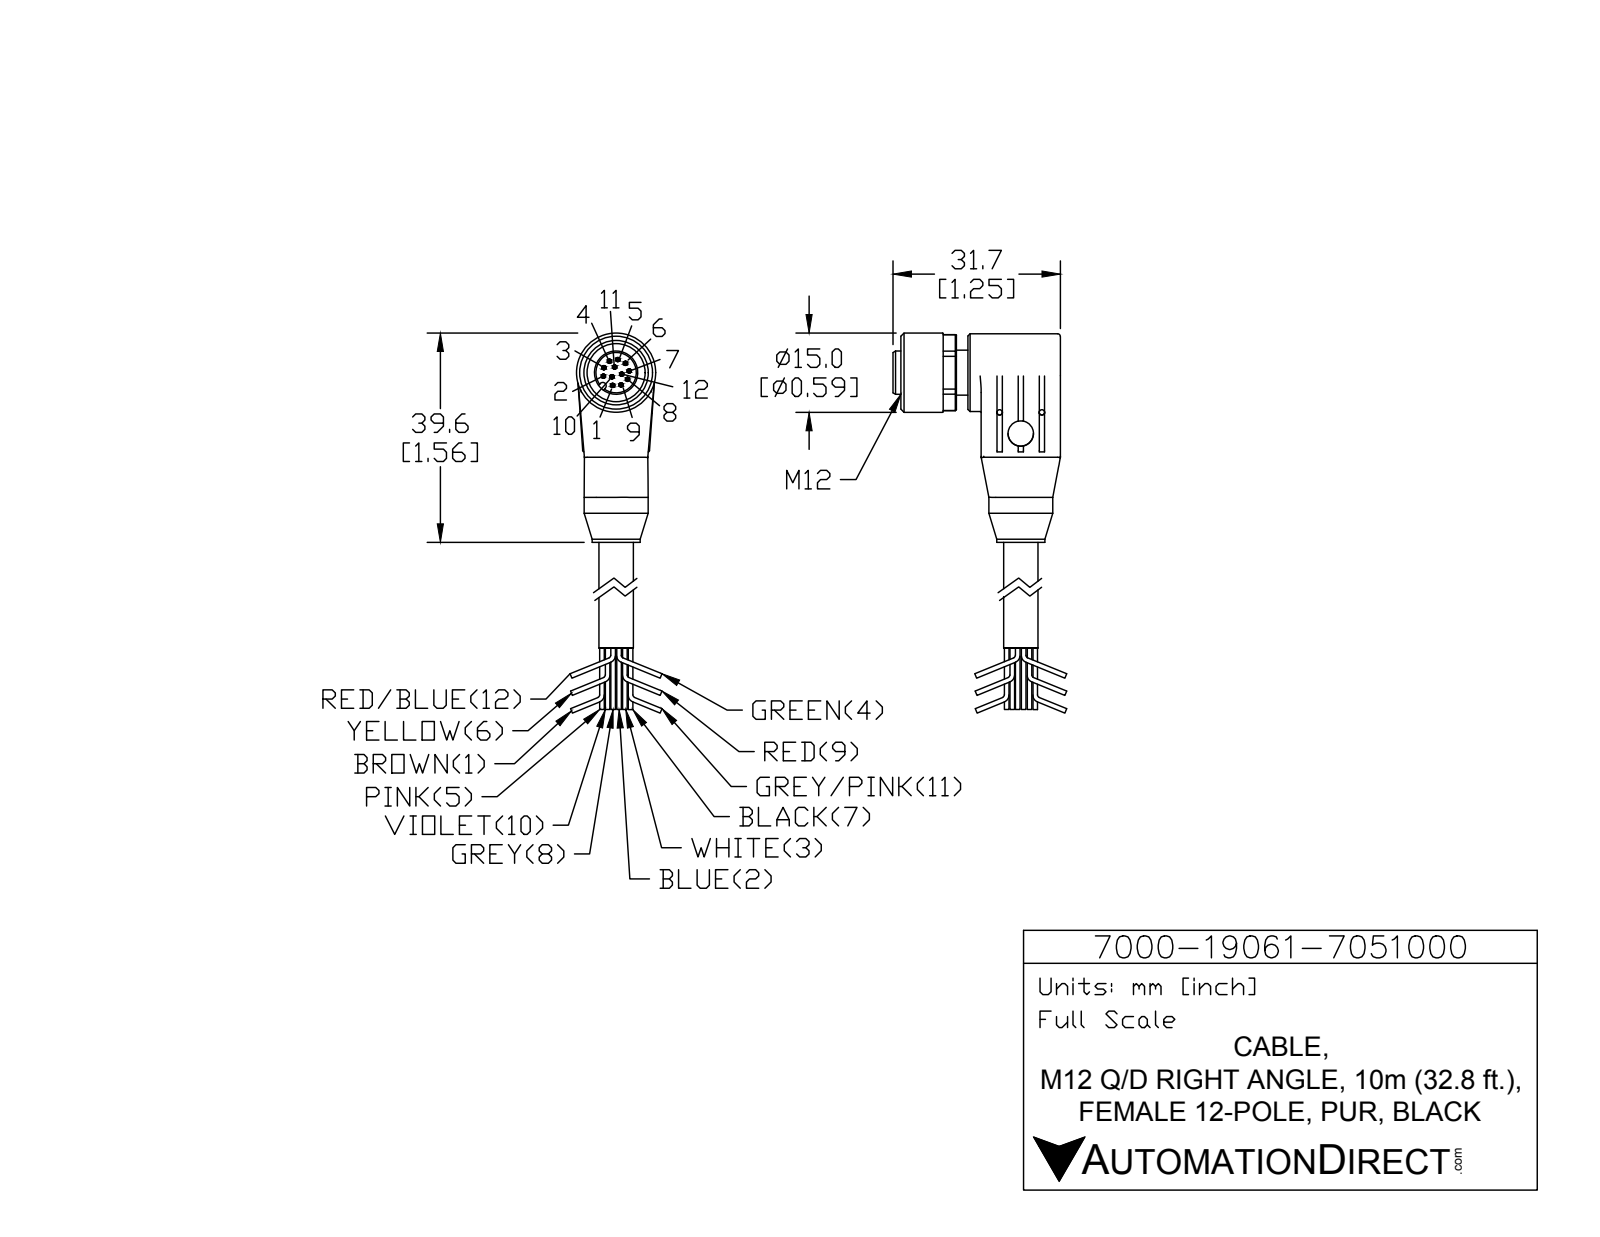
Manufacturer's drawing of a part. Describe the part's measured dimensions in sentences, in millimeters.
The part is named "7000-19061-7051000". Its 3-D file was written by "SolidWorks 2015 (AUTOMOTIVE_DESIGN)". It is 1 solid with 186 faces: 77 planar, 75 cylindrical and 34 other. Overall it measures 59.6 by 31.7 by 15 millimeters. Its volume is 9 096 cubic millimeters and its surface area 4 119 square millimeters. Round holes: 12 of diameter 0.8, 4 of diameter 1.05, 1 of diameter 4.8, 1 of diameter 11. Round bosses or shafts: 1 of diameter 15, 1 of diameter 14.7, 1 of diameter 12.1, 1 of diameter 9.1, 1 of diameter 8.5, 1 of diameter 8.2, 1 of diameter 6.5. Partial cylindrical surfaces (rounded edges, fillets, slot ends): 4 of radius 0.5, 2 of radius 0.3, 1 of radius 0.65, 1 of radius 7.2. The main face-to-face distances are 2.5, 15, 4.7, 17.5, 19.7, 2.2, 3, 7.7, 12, 16.7. The hole center spacings are 2.5, 1.61, 4.17, 3.05, 4.84, 4.99, 1.1, 4.61.
